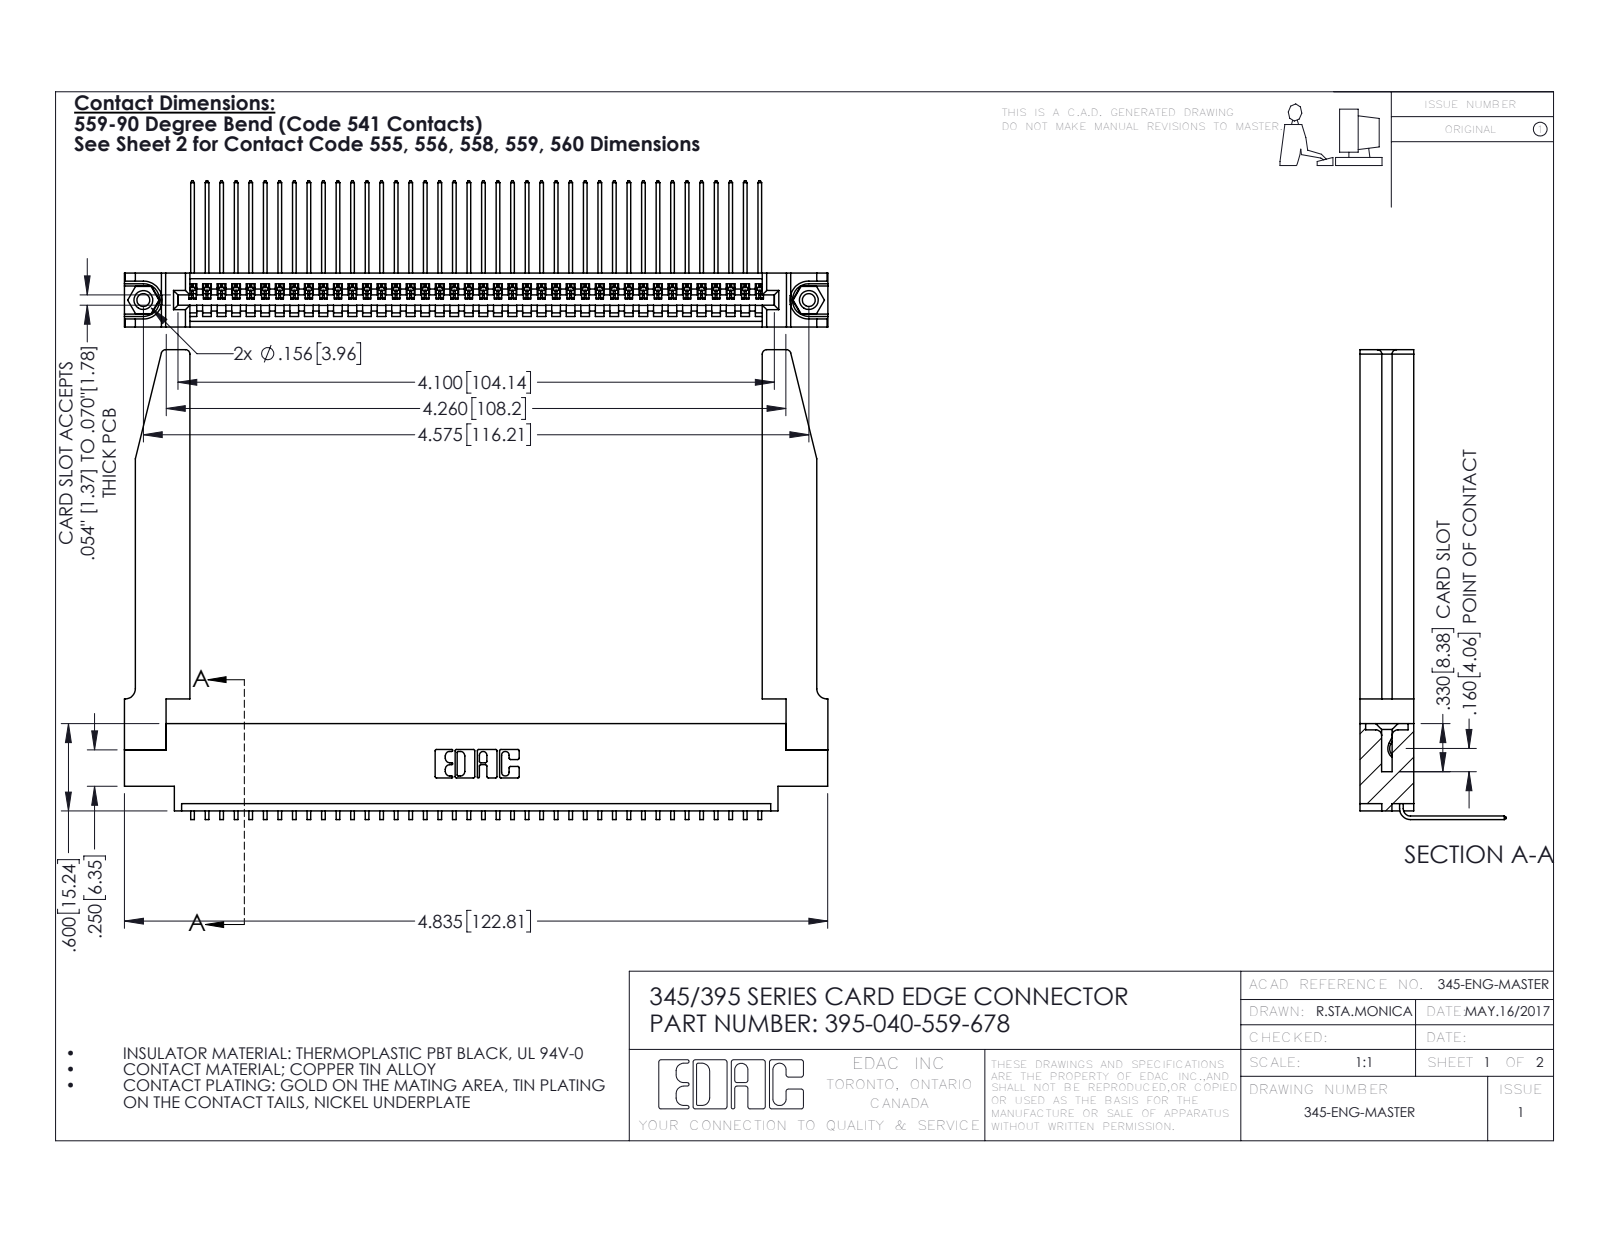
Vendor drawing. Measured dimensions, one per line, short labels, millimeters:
name: 345-220-078_345-220-078; 345-292-001_558 559 Tail - 1; 395-040-559-678; 345 Part_0.170 Offset - 0.156 Dia-TH (+1 more)
written by: SolidWorks 2016 (CONFIG_CONTROL_DESIGN)
unit: mm
bodies: 45 solids, 2764 faces (1906 planar, 806 cylindrical, 52 other)
size: 122.8 × 82 × 25.5
volume: 19 440 mm³; area: 23 240 mm²
holes: 2× ⌀2.3, 2× ⌀3.2, 2× ⌀4, 1× ⌀1.6
bosses: 2× ⌀3.9
rounds: 80× R0.2, 22× R0.3, 8× R0.8, 6× R0.2, 6× R0.8, 3× R0.7, 2× R0.8, 2× R1
face distances: 9.4, 1.8, 7.6, 2.5, 6.9, 0.6, 5.1, 5.7, 3.8, 3.8
hole spacings: 6.9, 110.2, 116.2
